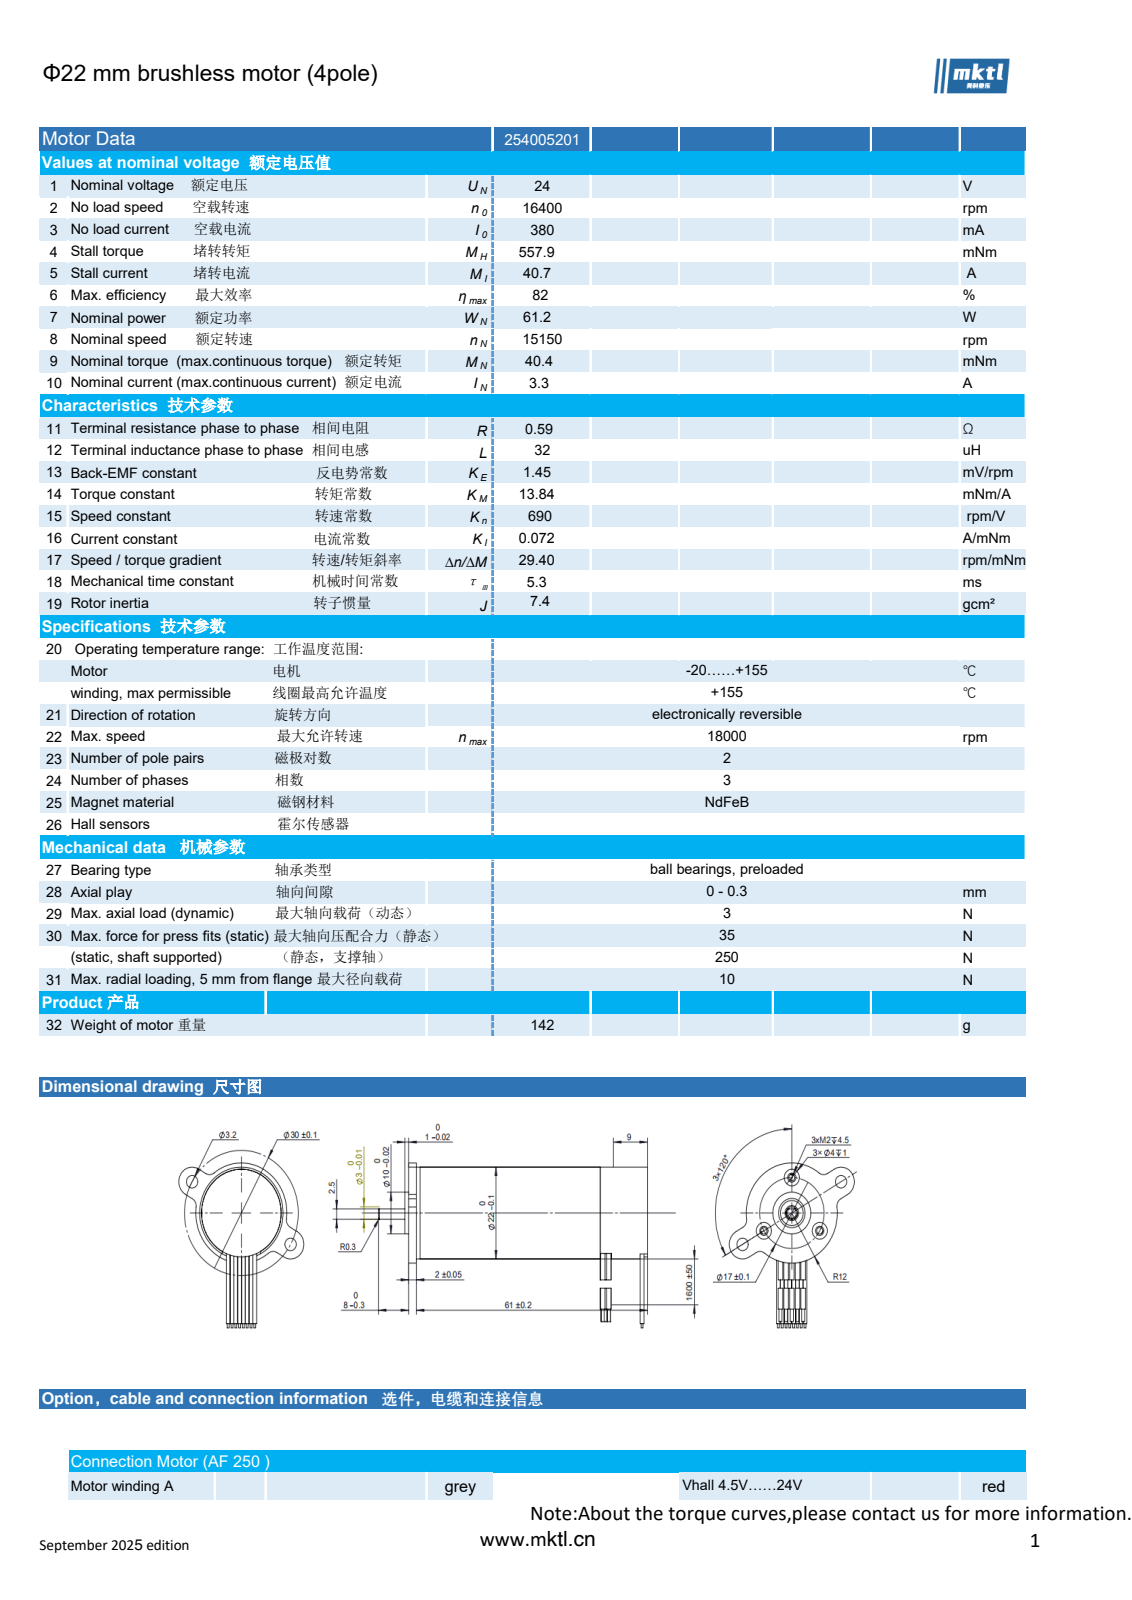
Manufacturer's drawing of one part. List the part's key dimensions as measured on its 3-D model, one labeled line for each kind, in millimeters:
Part name (STEP PRODUCT): 电机装配 254005201
STEP written by: SolidWorks 2018 (CONFIG_CONTROL_DESIGN)
Units: millimetres
Bodies: 188 solids, 1334 faces (525 planar, 776 cylindrical, 33 other)
Overall size (bounding box): 71 × 22 × 22
Volume: 17 642 mm³ · Surface area: 67 586 mm²
Round holes (diameter × count): ⌀1.6 ×7, ⌀0.7 ×5, ⌀2.2 ×2, ⌀3.1 ×2, ⌀3 ×1, ⌀6.5 ×1, ⌀7 ×1, ⌀8 ×1, ⌀13 ×1, ⌀13.2 ×1, ⌀16.4 ×1, ⌀16.5 ×1
Round bosses / shafts (diameter × count): ⌀0.3 ×3, ⌀22 ×1, ⌀20.9 ×1, ⌀20.8 ×1, ⌀19.5 ×1, ⌀16.3 ×1, ⌀12.7 ×1, ⌀12.5 ×1
Partial cylindrical surfaces — rounded edges, fillets, slot ends (radius × count): R0.2 ×2, R1 ×2
Main face-to-face distances: 0.4, 0.6, 1, 0.8, 1.2, 1.4, 1.6, 1.8, 2, 2.2
Hole centre spacings: 1.5, 15.79, 3, 8.5, 14.72, 2.38, 4.5, 4.64
